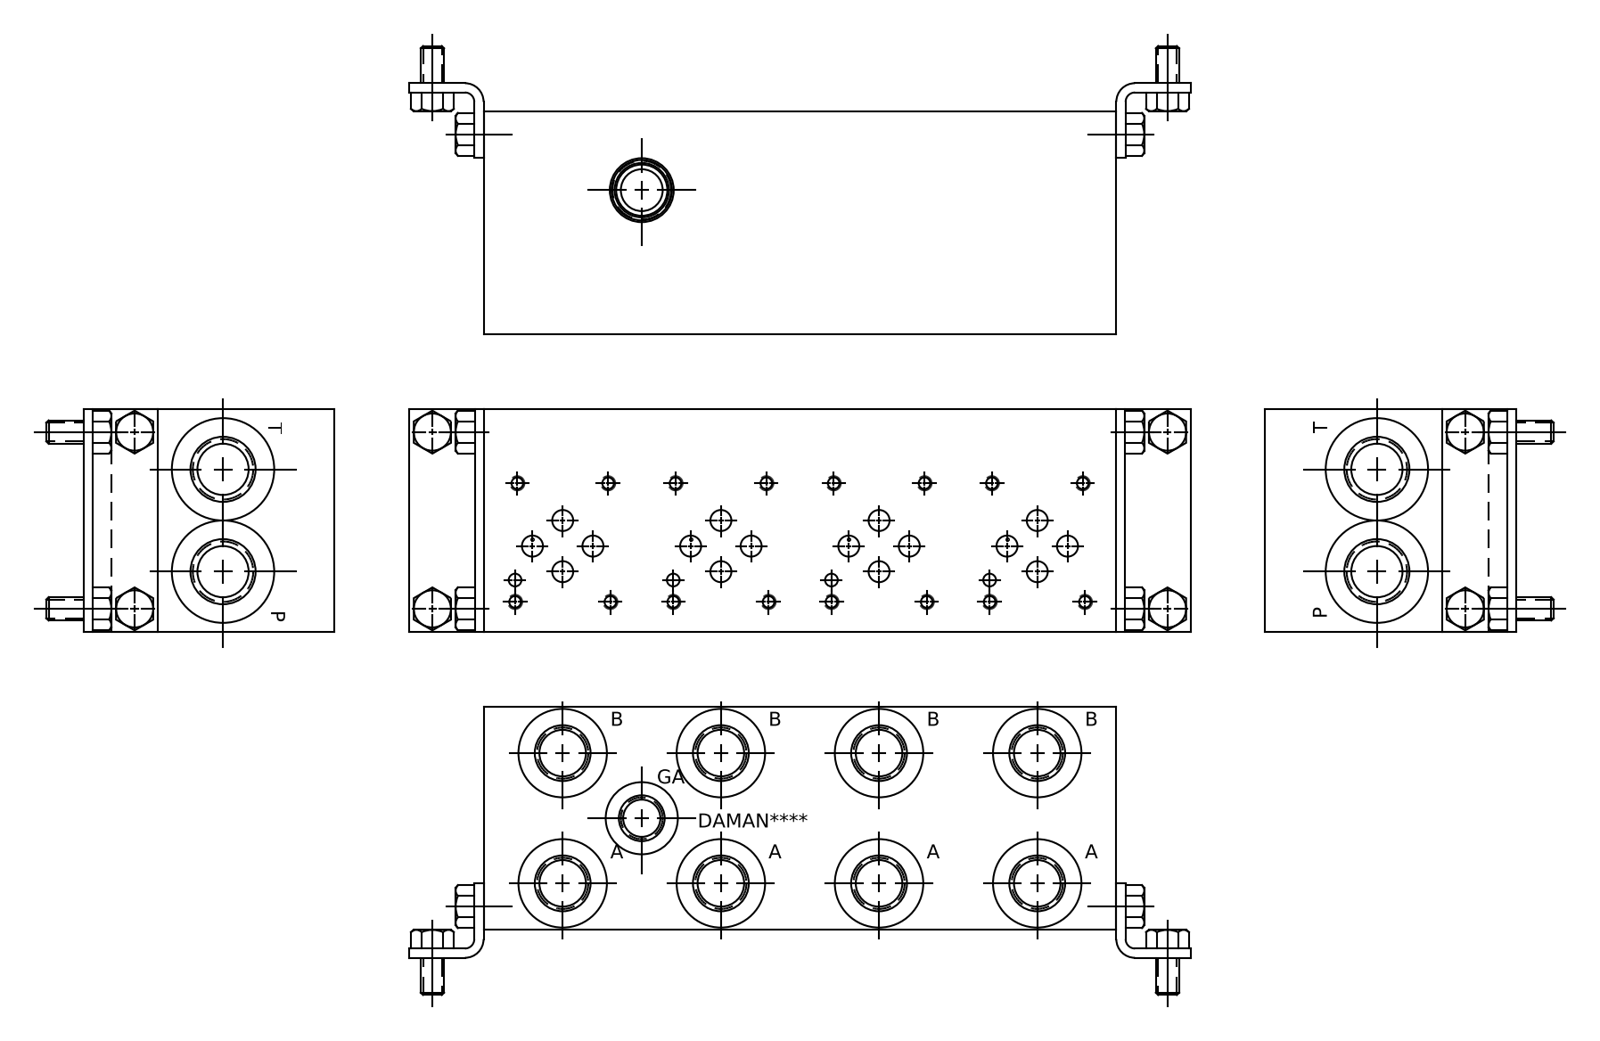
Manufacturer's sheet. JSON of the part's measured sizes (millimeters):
{"part_name": "Part_AD03P052S_S_3D", "step_written_by": "Autodesk Inventor 2020 (AUTOMOTIVE_DESIGN)", "units": "millimeters", "bodies": {"solids": 1, "faces": 863, "planar": 441, "cylindrical": 131, "other": 291}, "overall_size": [215.9, 76.2, 76.2], "volume_mm3": 1133000, "surface_area_mm2": 105983, "round_holes": [[3.78, 16], [4.83, 16], [7.14, 12], [15.88, 8], [17.5, 8], [19.05, 8], [19.25, 8], [30.63, 8], [3.96, 4], [6.35, 4], [6.53, 3], [7.92, 3]], "face_to_face_distances": [76.2, 0.79, 215.9, 75.41, 215.11, 214.32, 14.27, 61.14, 15.06, 0.75], "hole_center_spacings": [107.95, 53.97, 53.98, 13.52, 19.95, 22.05, 33.55, 51.45]}
